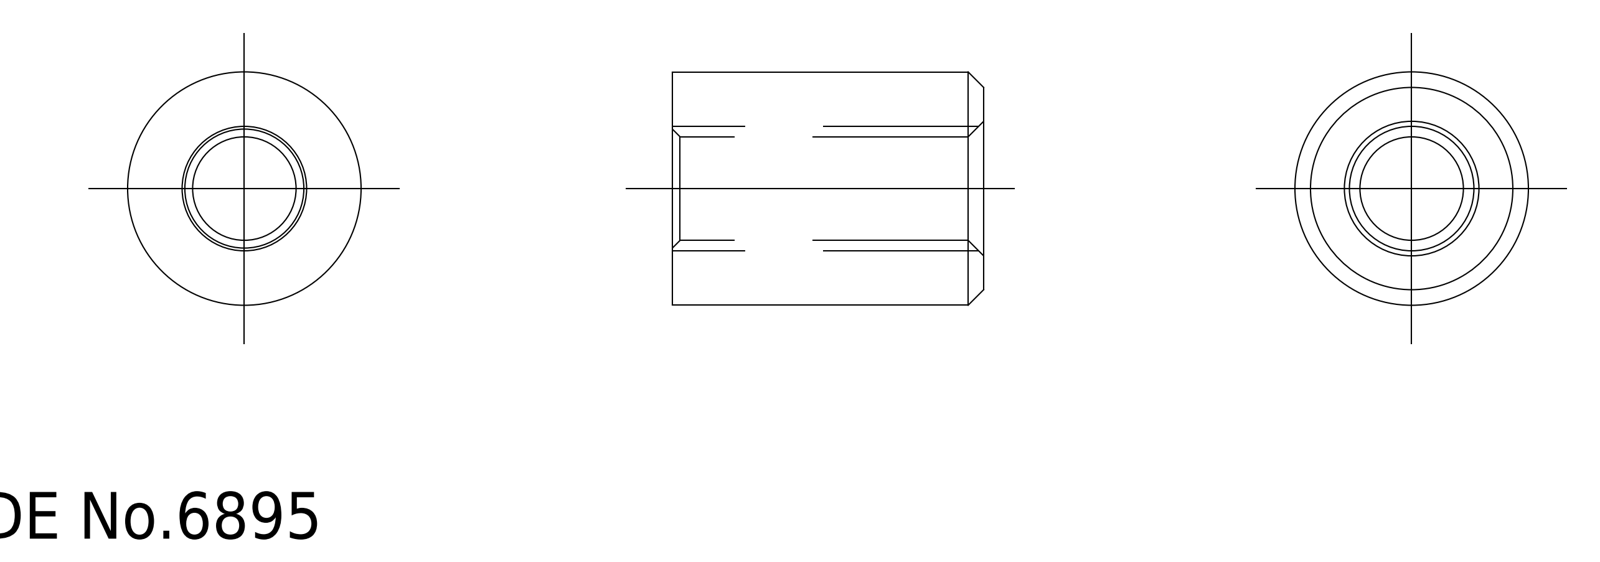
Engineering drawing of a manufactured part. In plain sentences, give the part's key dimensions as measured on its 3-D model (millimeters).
The part is named "boss". Its 3-D file was written by "CADfix (AUTOMOTIVE_DESIGN)". It is 1 solid with 10 faces: 0 planar, 0 cylindrical and 10 other. Overall it measures 20 by 15 by 15 millimeters. Its volume is 2 510 cubic millimeters and its surface area 1 665 square millimeters.
